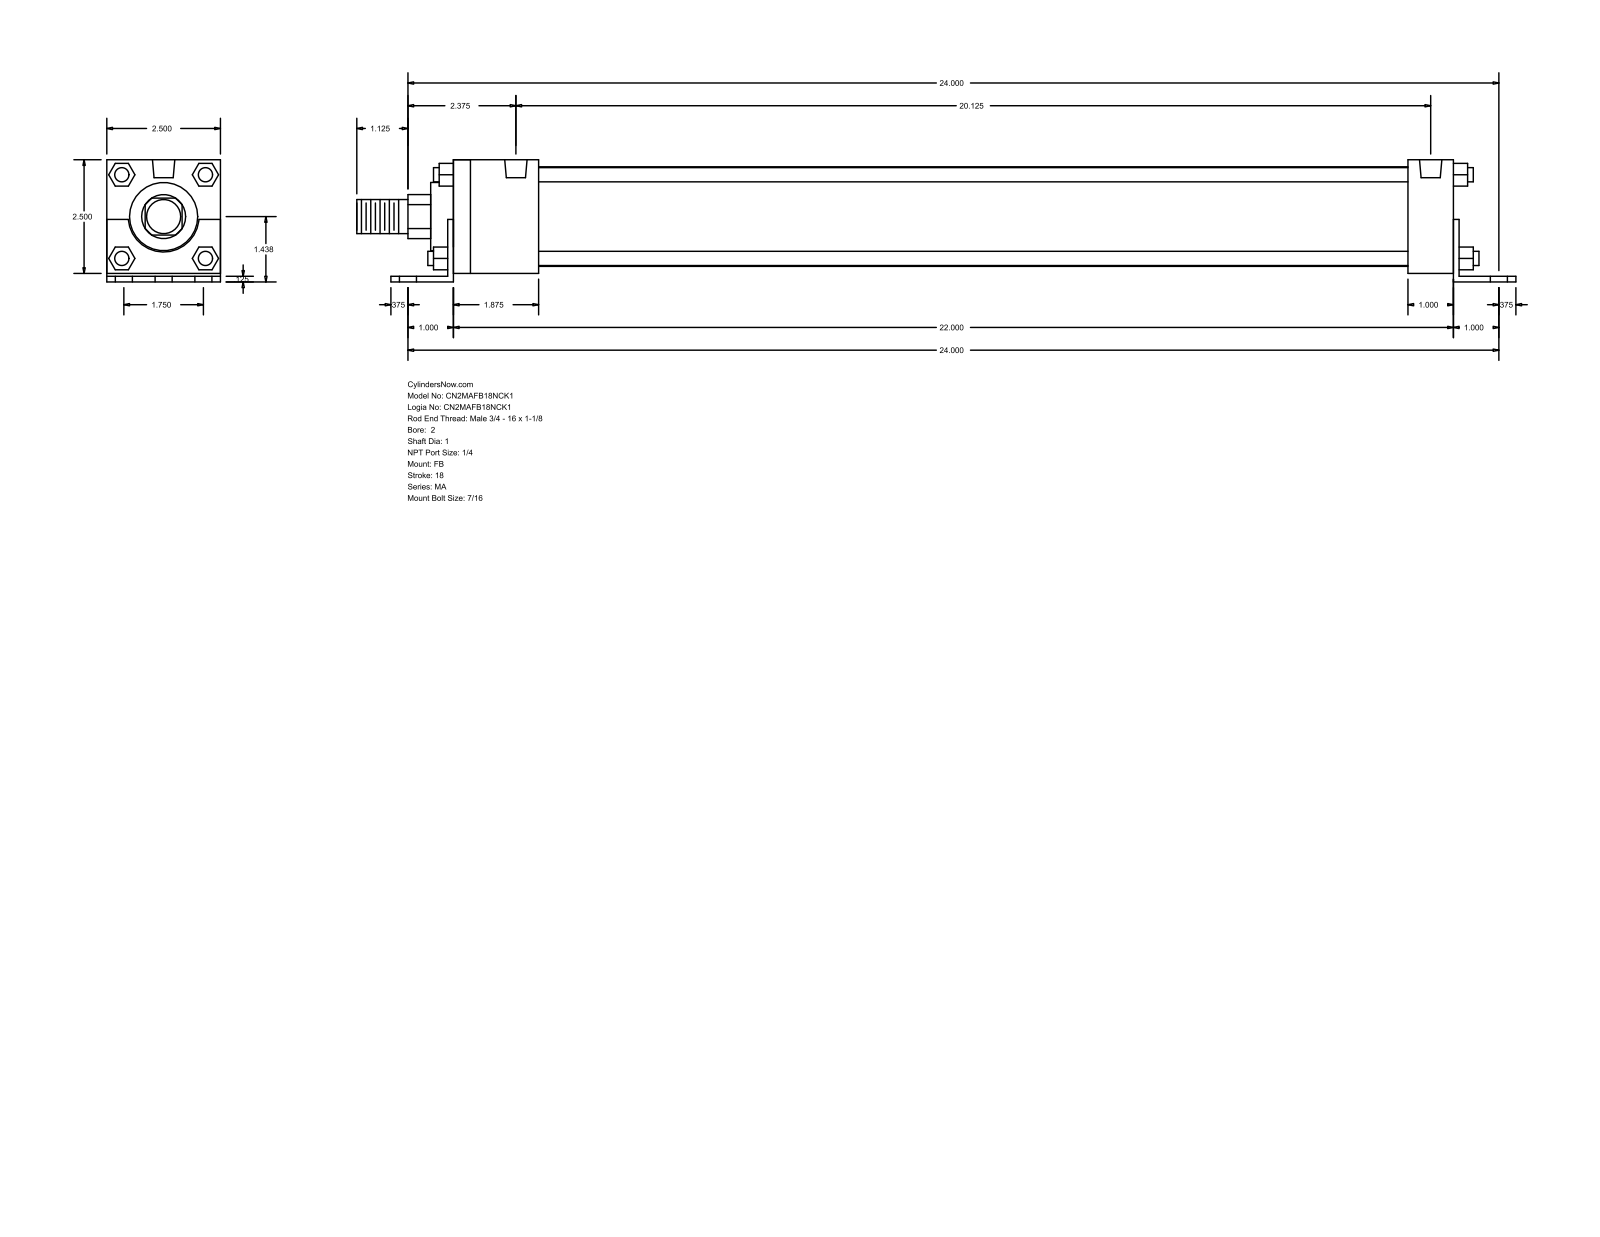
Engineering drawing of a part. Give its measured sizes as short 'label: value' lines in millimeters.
name: MA_FB__0200_1
written by: GSSL Pune (CONFIG_CONTROL_DESIGN)
unit: mm
bodies: 0 solids, 140 faces (105 planar, 35 cylindrical, 0 other)
size: 647.7 × 68.26 × 63.5
holes: 6× ⌀11.11, 4× ⌀7.94, 2× ⌀12.49
bosses: 4× ⌀7.94, 1× ⌀55.63, 1× ⌀38.1, 1× ⌀25.4, 1× ⌀19.05
rounds: 1× R12.29, 1× R19.81
face distances: 63.5, 3.17, 4.76, 68.26, 1.59, 65.09, 12.7, 3.18, 558.8, 561.98
hole spacings: 22.23, 610.01, 609.6, 44.11, 44.46, 64.3, 511.17, 549.72
